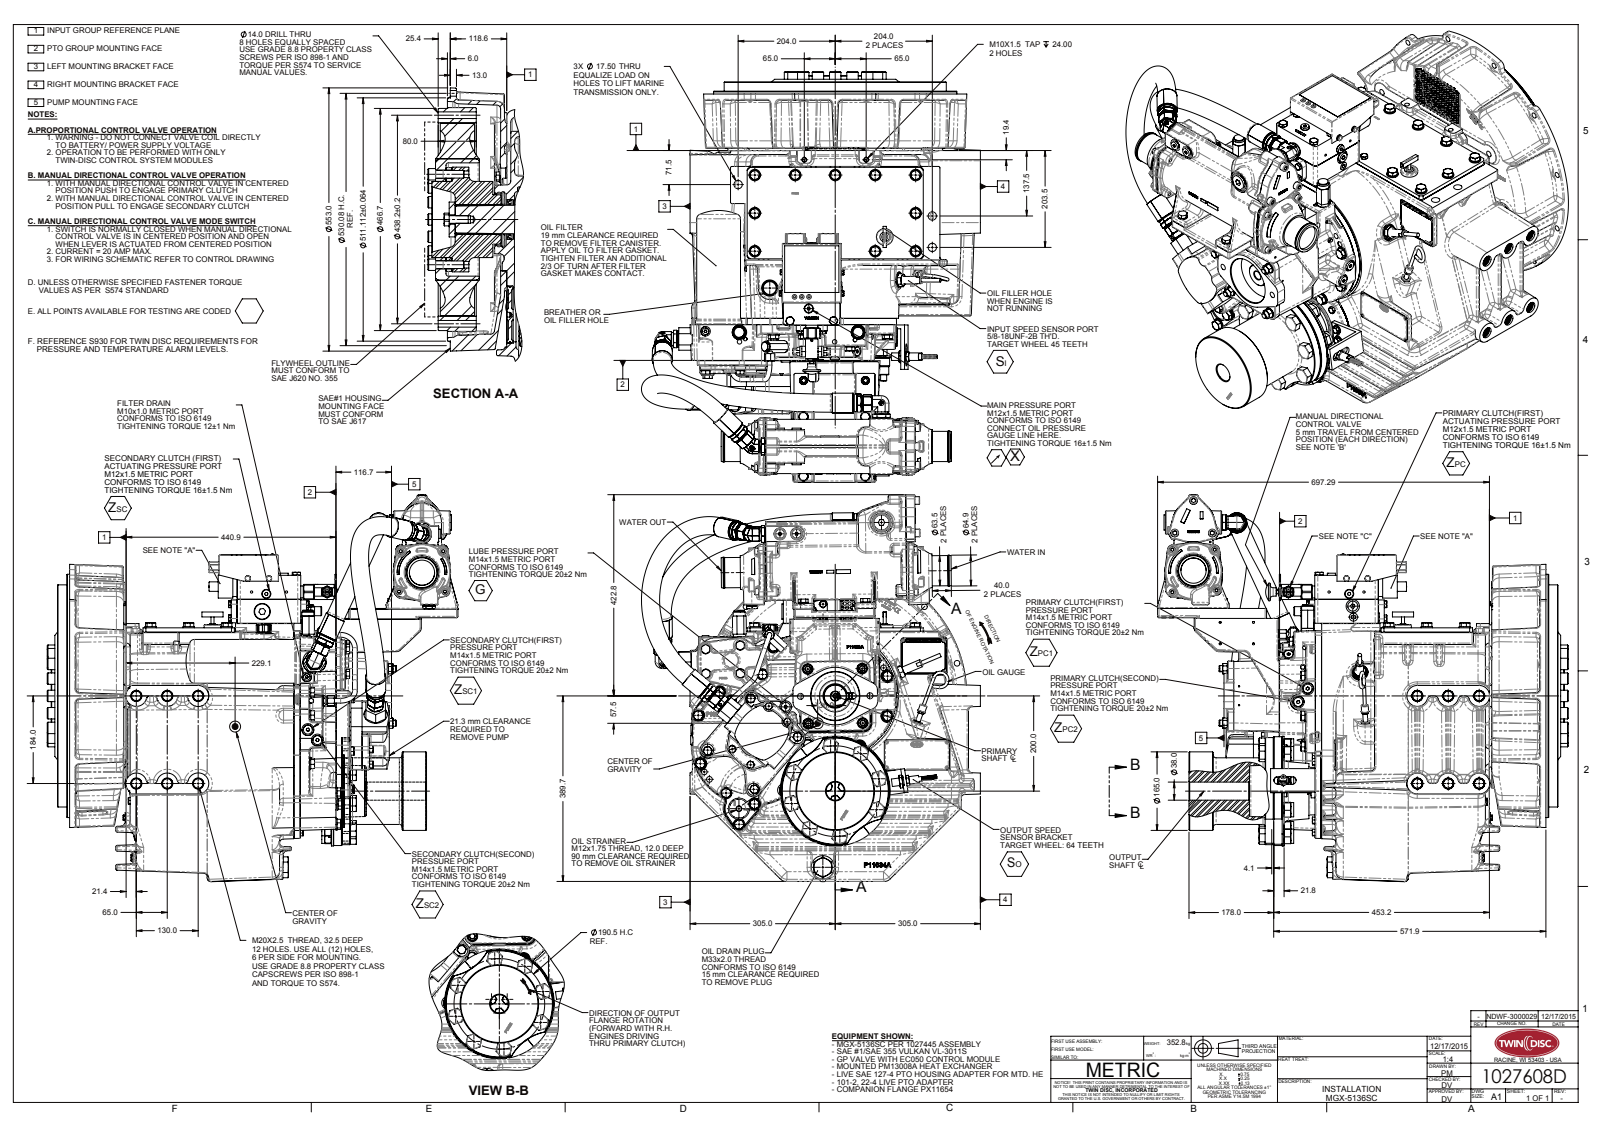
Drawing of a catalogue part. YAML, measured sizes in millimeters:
part_name: "1027608D"
step_written_by: "SolidWorks 2010 (AUTOMOTIVE_DESIGN)"
units: millimeters
bodies: {solids: 0, faces: 6690, planar: 2061, cylindrical: 1970, other: 2659}
overall_size: [862.91, 813.09, 712.14]
round_holes:
  - {diameter: 7, count: 82}
  - {diameter: 11.91, count: 12}
  - {diameter: 14, count: 10}
  - {diameter: 10, count: 8}
  - {diameter: 25, count: 8}
  - {diameter: 4.2, count: 5}
  - {diameter: 6.75, count: 5}
  - {diameter: 20, count: 5}
  - {diameter: 23.51, count: 5}
  - {diameter: 27, count: 5}
  - {diameter: 8.8, count: 4}
  - {diameter: 7.71, count: 3}
round_bosses_or_shafts:
  - {diameter: 24, count: 39}
  - {diameter: 30, count: 8}
  - {diameter: 19.85, count: 8}
  - {diameter: 18.9, count: 8}
  - {diameter: 13, count: 8}
  - {diameter: 10, count: 6}
  - {diameter: 31.8, count: 5}
  - {diameter: 41.91, count: 4}
partial_cylinders:
  - {radius: 3, count: 146}
  - {radius: 4, count: 137}
  - {radius: 2, count: 82}
  - {radius: 8, count: 72}
  - {radius: 2.5, count: 70}
  - {radius: 5, count: 61}
  - {radius: 6.5, count: 42}
  - {radius: 10, count: 26}
face_to_face_distances: [0.39, 13.09, 13.48, 357.48, 357.09, 344, 370.82, 370.43, 357.34, 13.34]
hole_center_spacings: [459.05, 137.19, 265.04, 374.81, 512.01, 130.01, 16, 65]
